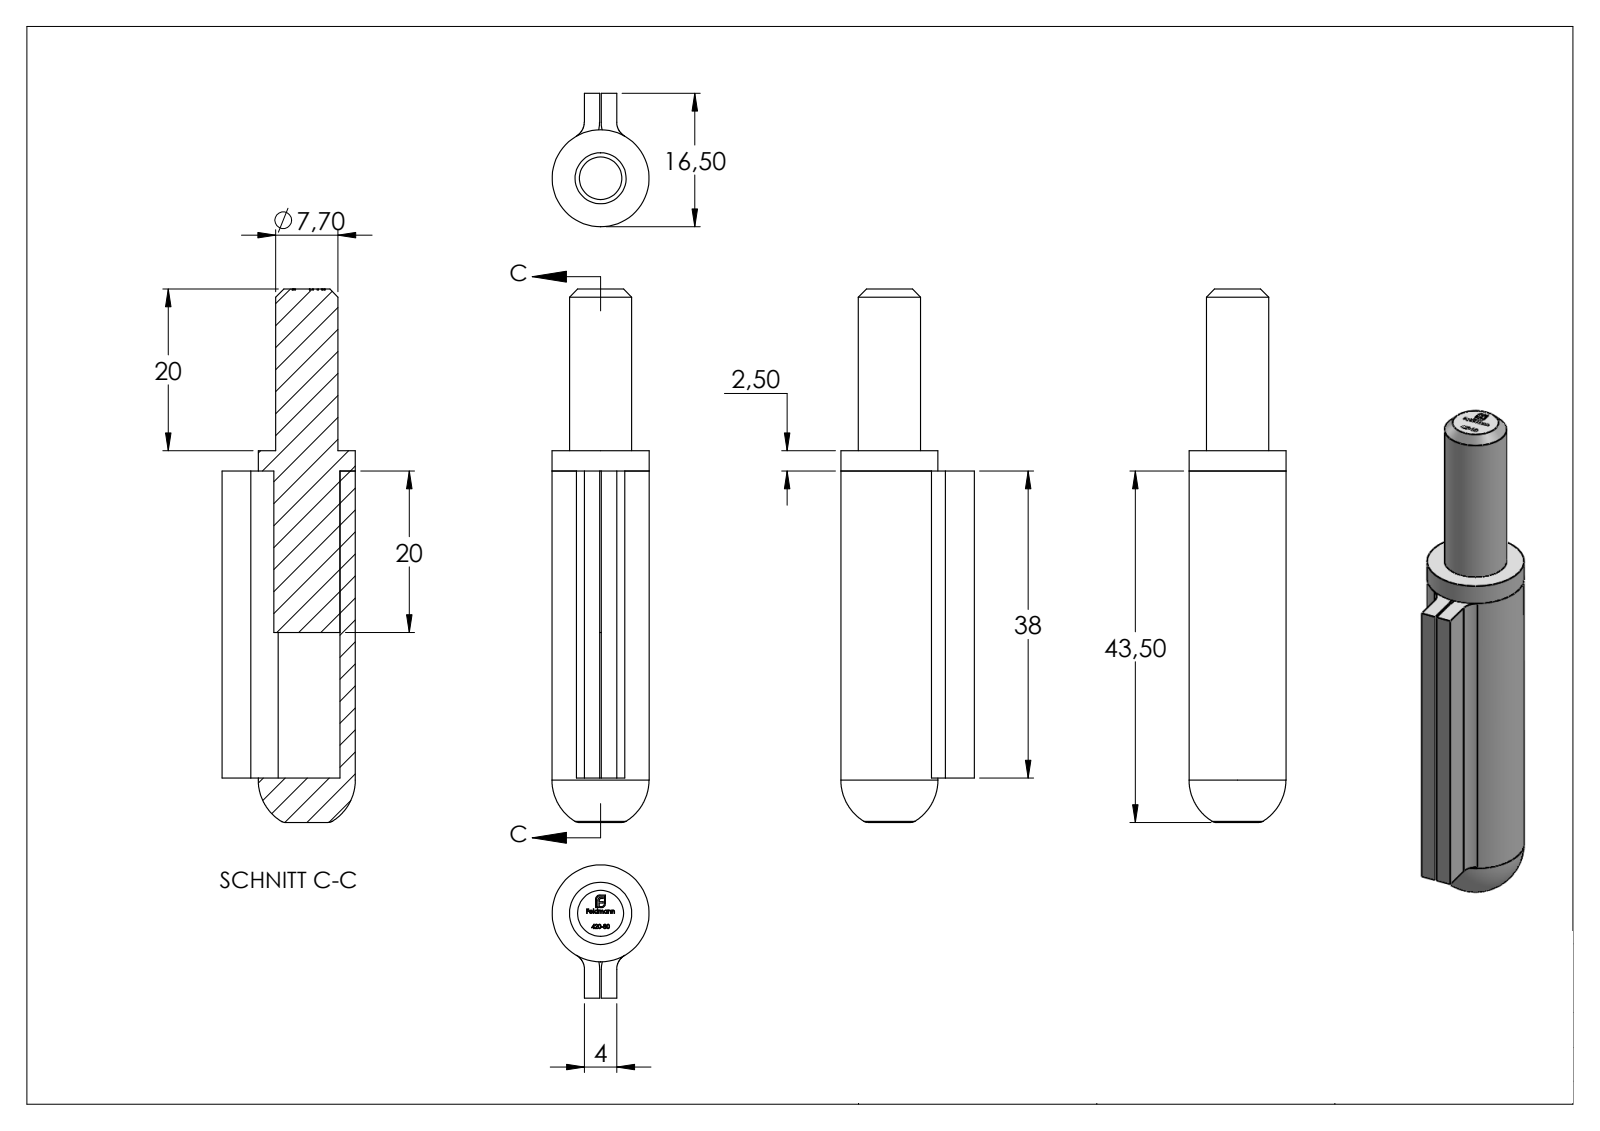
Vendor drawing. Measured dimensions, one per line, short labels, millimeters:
name: 420-XX Teil2; 420-XX Teil2_420-80 Teil2; 420-XX Teil1_420-80 Teil1; 420-80 (+1 more)
written by: SolidWorks 2018 (CONFIG_CONTROL_DESIGN)
unit: mm
bodies: 3 solids, 289 faces (148 planar, 22 cylindrical, 119 other)
size: 89.5 × 16.5 × 12
volume: 8 942 mm³; area: 8 407 mm²
holes: 1× ⌀8.2
bosses: 1× ⌀12, 1× ⌀7.7
rounds: 2× R2, 2× R3.9
face distances: 1.9, 2.1, 4, 38, 40.5, 2.5, 18, 60.5, 20, 22.5
